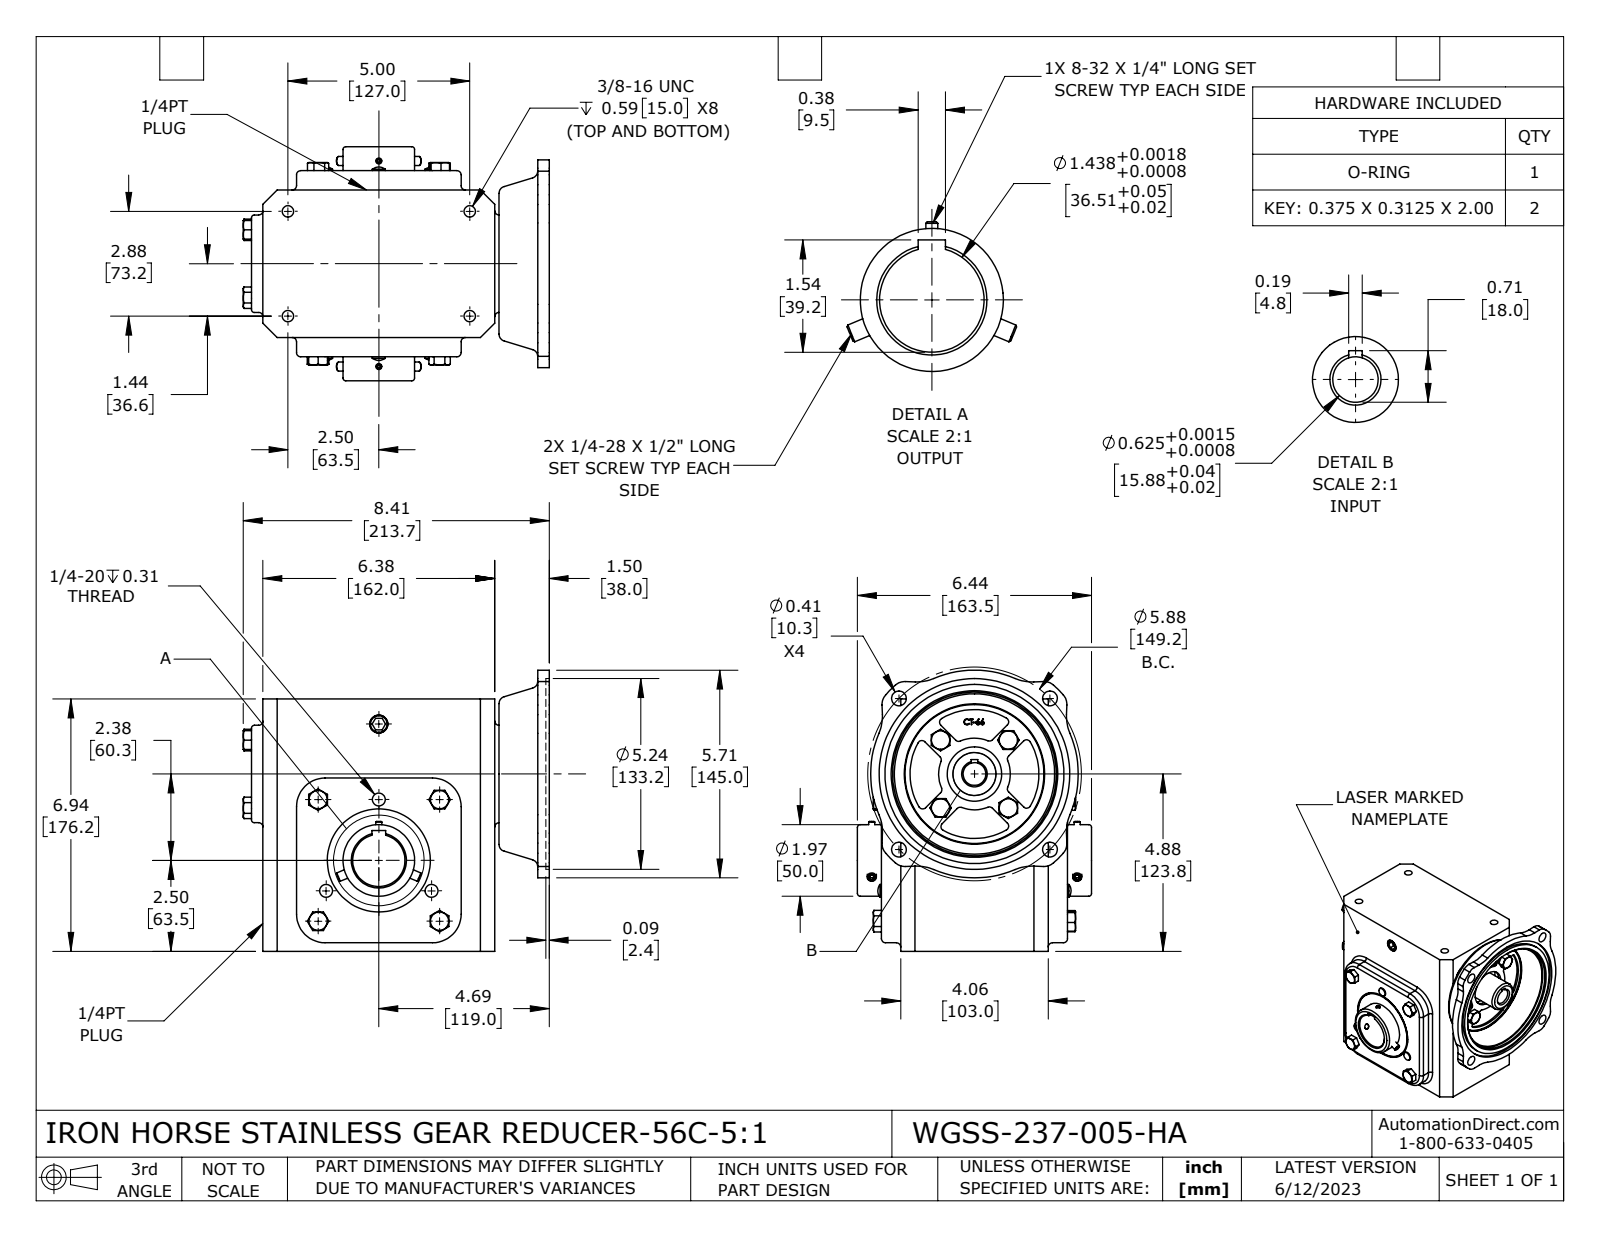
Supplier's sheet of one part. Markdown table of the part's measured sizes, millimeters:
| quantity | value |
| --- | --- |
| part name | WGSS-237-005-HA |
| STEP written by | SolidWorks 2021 (CONFIG_CONTROL_DESIGN) |
| units | millimeters |
| bodies | 7 solids, 670 faces (287 planar, 195 cylindrical, 188 other) |
| overall size | 213.7 × 196.3 × 163.5 |
| volume | 3 351 000 mm³ |
| surface area | 224 600 mm² |
| round holes (diameter × count) | 5.4 × 4, 8 × 4, 10.3 × 4, 3.5 × 2, 15.9 × 1, 22 × 1, 36.5 × 1, 36.6 × 1, 38 × 1, 45 × 1, 97 × 1, 114.3 × 1 |
| round bosses / shafts (diameter × count) | 6.4 × 4, 9 × 3, 4.2 × 2, 125 × 1, 72 × 1, 50 × 1, 30 × 1 |
| partial cylindrical surfaces (radius × count) | 3 × 40, 10 × 12, 30 × 8, 2 × 4, 20 × 4, 25 × 1, 45 × 1, 72.5 × 1 |
| main face-to-face distances | 13.5, 116.5, 176.2, 8, 103, 162, 130, 200, 30, 170 |
| hole center spacings | 72.6, 74.6, 125.6, 143.5, 73.2, 105.5, 105.5, 127 |
